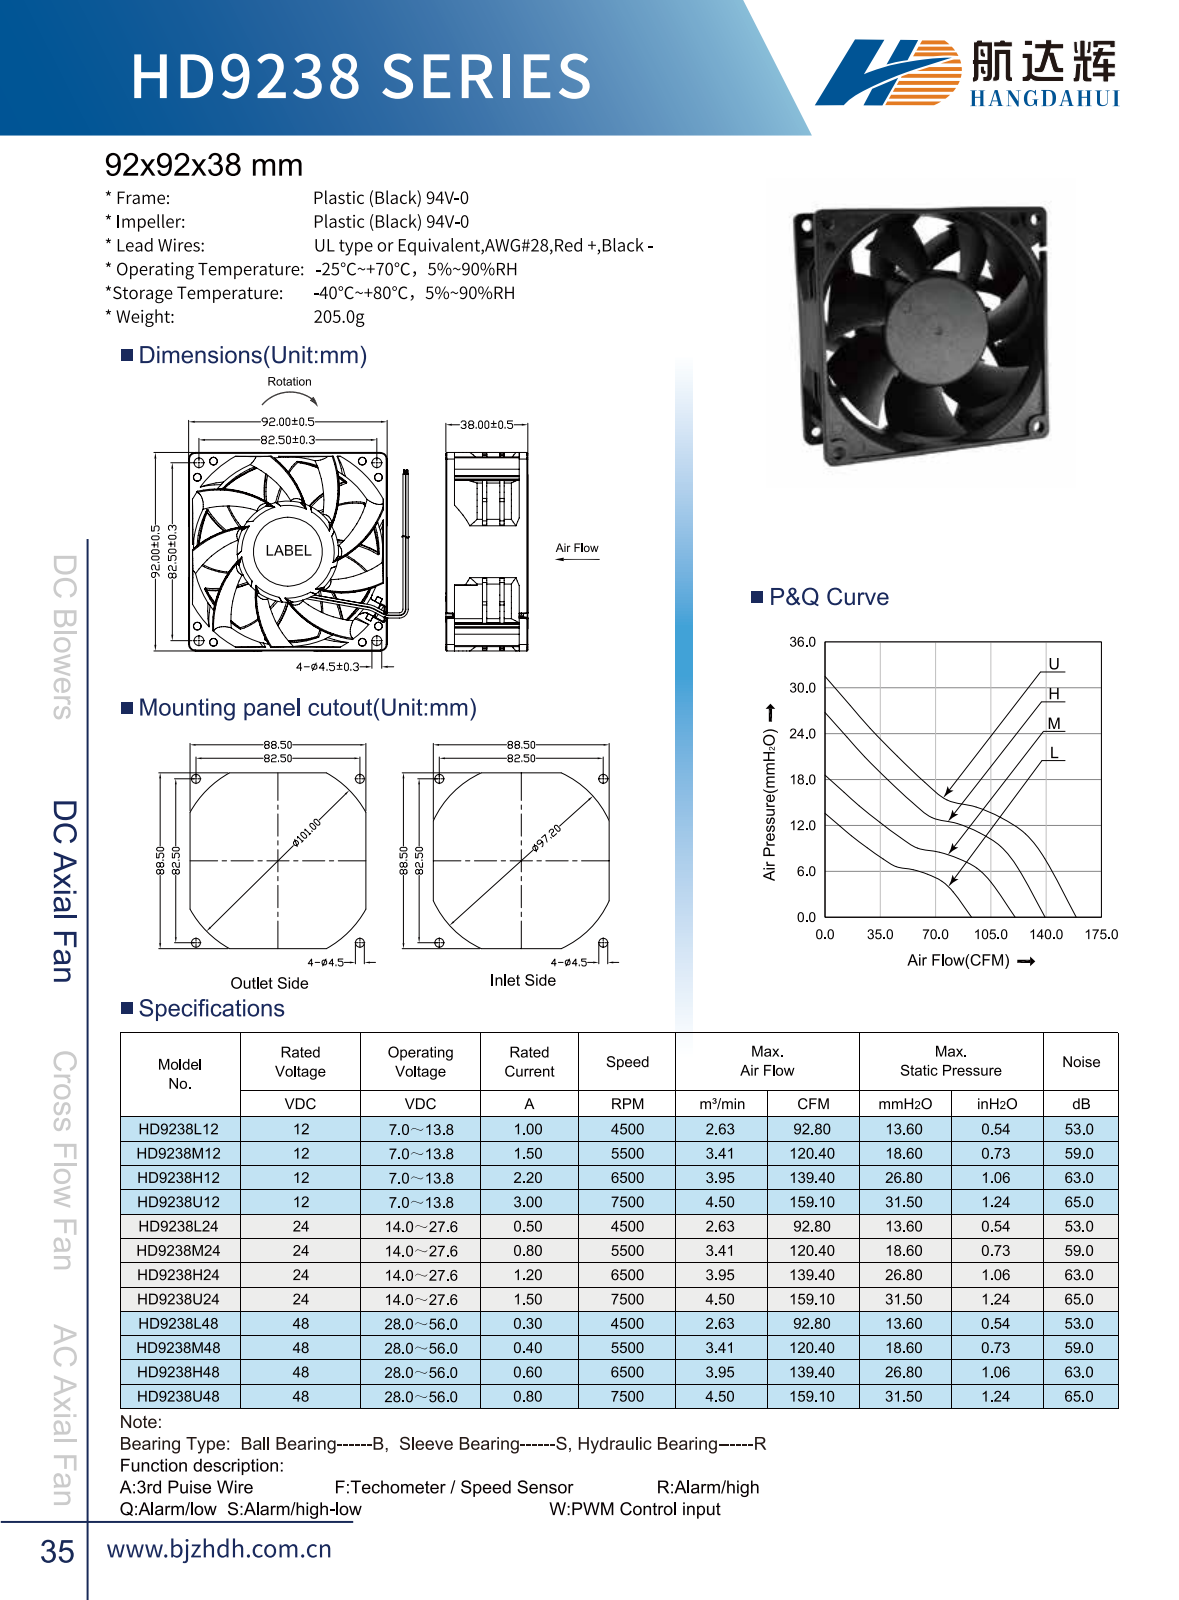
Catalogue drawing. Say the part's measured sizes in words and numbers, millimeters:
The part is named "9238-外框". Its 3-D file was written by "SIEMENS PLM Software NX 10.0 (AUTOMOTIVE_DESIGN)". It is 1 solid with 1081 faces: 384 planar, 249 cylindrical and 448 other. Overall it measures 92 by 92 by 38.32 millimeters. Its volume is 39 876 cubic millimeters and its surface area 50 865 square millimeters. Round holes: 4 of diameter 4.5, 1 of diameter 10. Partial cylindrical surfaces (rounded edges, fillets, slot ends): 61 of radius 0.2, 14 of radius 0.4, 5 of radius 1, 4 of radius 0.75, 4 of radius 4, 3 of radius 0.6, 3 of radius 5.5, 2 of radius 0.5. The main face-to-face distances are 92, 1.85, 90.15, 1.65, 32.51, 28.2, 1.75, 90.25, 88.4, 4.5. The hole center spacings are 58.34, 82.5, 116.67.
